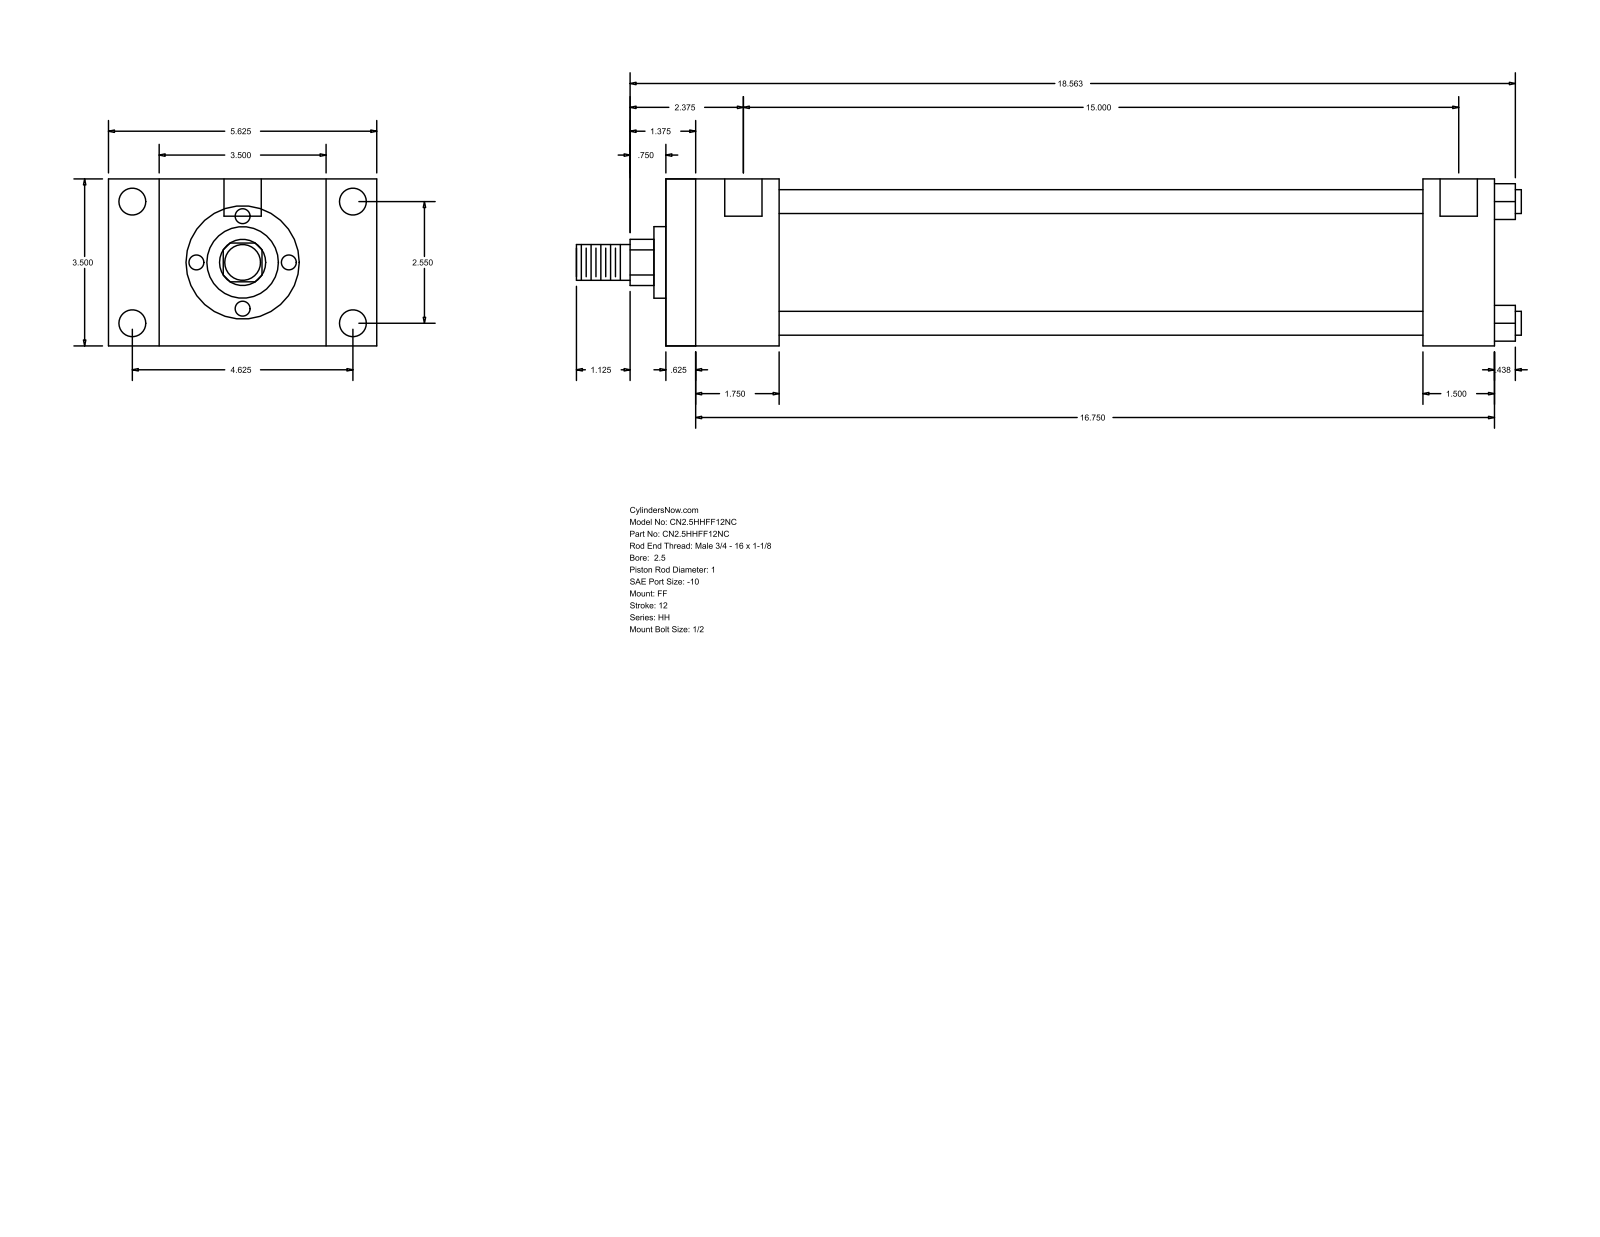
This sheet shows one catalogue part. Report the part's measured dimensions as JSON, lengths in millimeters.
{"part_name": "HH_FF__0250_1", "step_written_by": "GSSL Pune (CONFIG_CONTROL_DESIGN)", "units": "millimeters", "bodies": {"solids": 0, "faces": 92, "planar": 64, "cylindrical": 28, "other": 0}, "overall_size": [503.24, 142.88, 88.9], "round_holes": [[5.56, 4], [14.3, 4], [19.84, 2]], "round_bosses_or_shafts": [[12.7, 4], [73.03, 1], [38.1, 1], [25.4, 1], [19.05, 1]], "partial_cylinders_radius": [[12.29, 1]], "face_to_face_distances": [88.9, 441.33, 15.87, 425.46, 60.33, 44.46, 381, 403.22, 387.35, 342.89], "hole_center_spacings": [1.59, 64.76, 117.48, 134.15, 382.58, 384.17, 380.99]}
